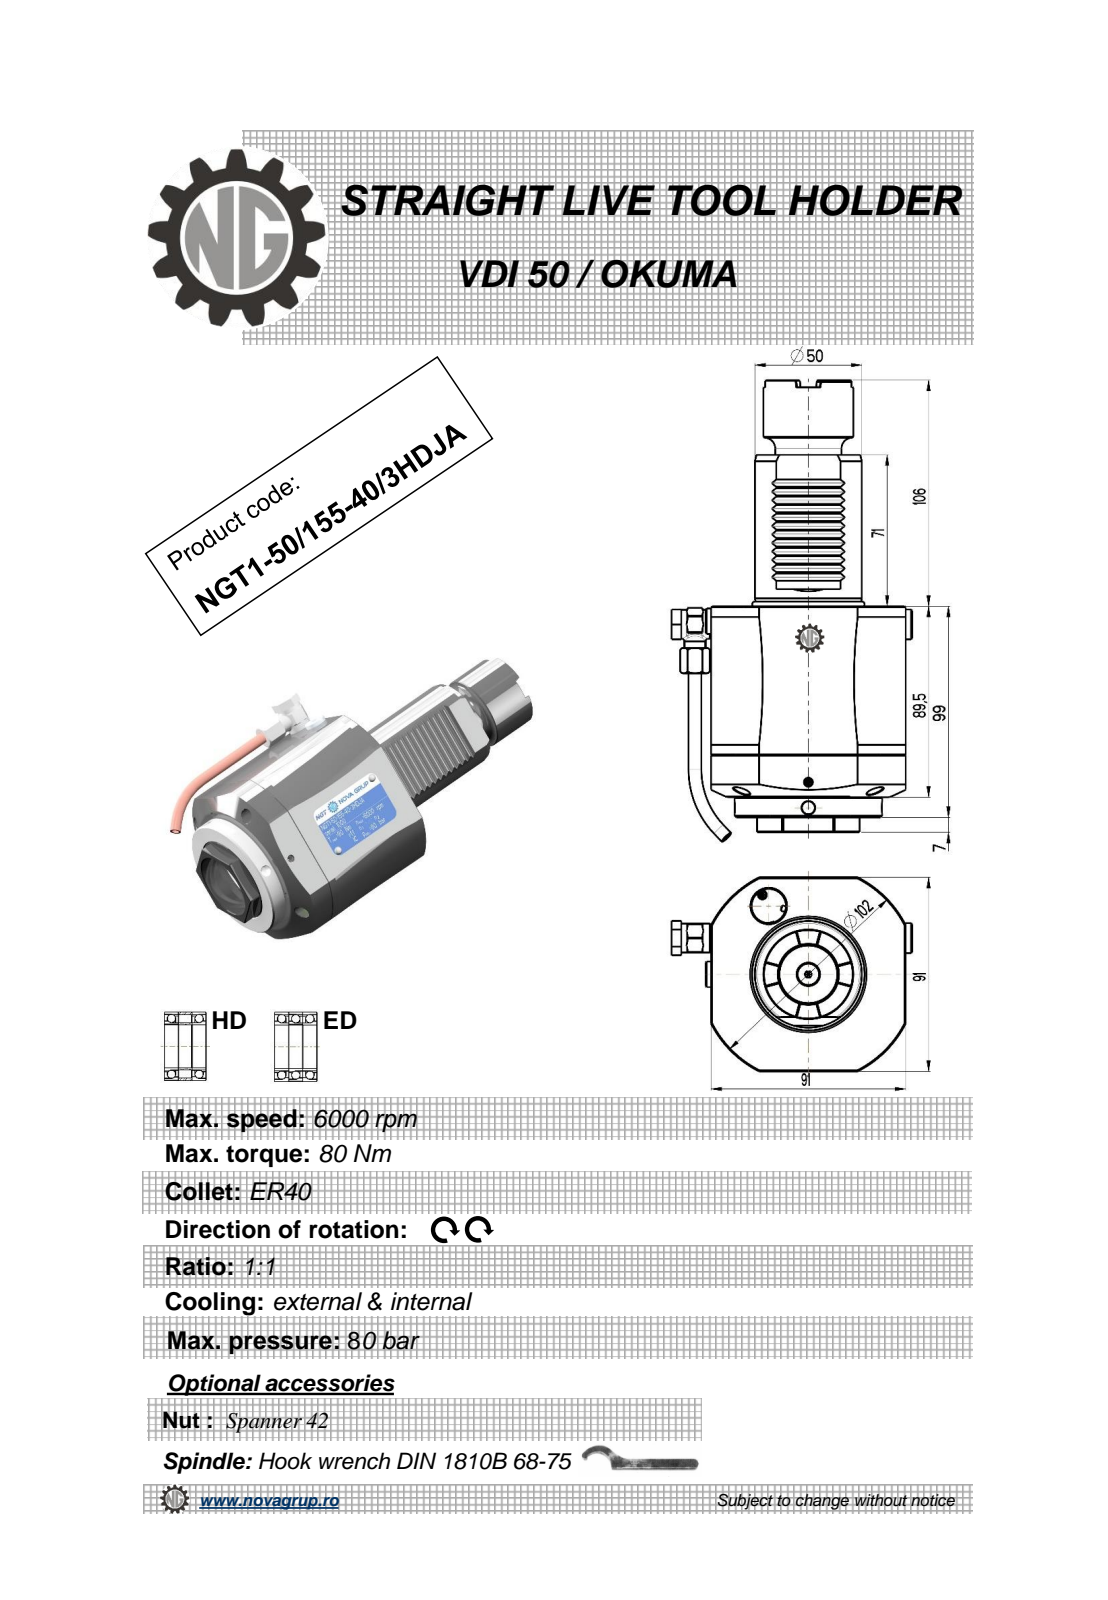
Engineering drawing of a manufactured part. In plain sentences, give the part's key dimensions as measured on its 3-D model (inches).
The part is named "NGT1_50_155_40_3HDJA". Its 3-D file was written by "PRO/ENGINEER BY PARAMETRIC TECHNOLOGY CORPORATION, 2010280 (CONFIG_CONTROL_DESIGN)". It is 1 solid with 415 faces: 159 planar, 104 cylindrical and 152 other. Overall it measures 8.521 by 4.425 by 3.583 inches. Its volume is 52.66 cubic inches and its surface area 109.9 square inches. Round holes: 3 of diameter 0.157, 2 of diameter 0.236, 1 of diameter 0.118, 1 of diameter 0.244, 1 of diameter 0.354, 1 of diameter 0.394, 1 of diameter 0.433, 1 of diameter 1.102, 1 of diameter 1.425, 1 of diameter 1.654. Round bosses or shafts: 2 of diameter 0.236, 1 of diameter 2.717, 1 of diameter 1.969, 1 of diameter 1.22, 1 of diameter 0.551, 1 of diameter 0.535, 1 of diameter 0.512, 1 of diameter 0.472. Partial cylindrical surfaces (rounded edges, fillets, slot ends): 12 of radius 0.012, 6 of radius 0.016, 4 of radius 0.02, 1 of radius 0.246, 1 of radius 0.303, 1 of radius 0.945, 1 of radius 2.008. The main face-to-face distances are 3.583, 3.524, 0.374, 3.898, 0.111, 6.693, 6.319, 2.795, 0.557, 0.445. The hole center spacings are 0.016, 2.191, 2.206, 3.451.
